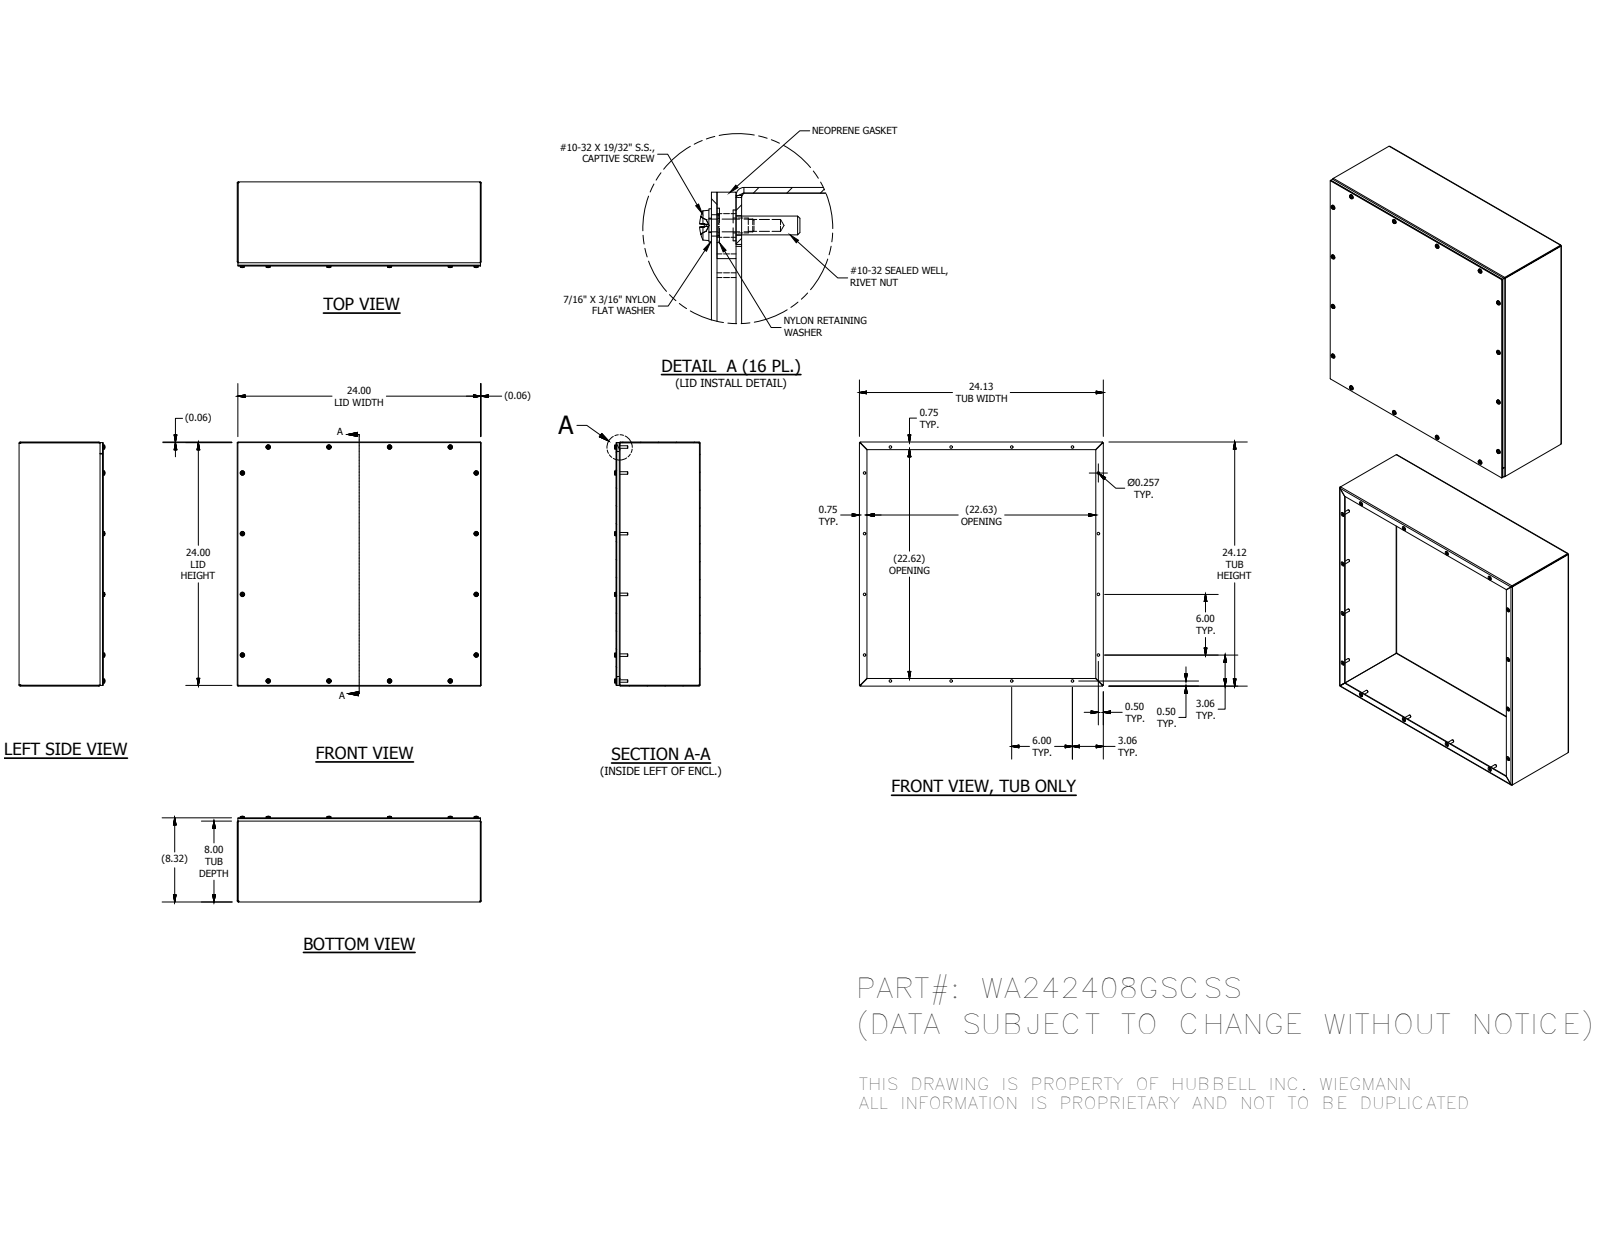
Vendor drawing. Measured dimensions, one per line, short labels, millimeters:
name: WA242408GSCSSBKP; WA2424GSCSSLID; 37210; 39035 (+4 more)
written by: Autodesk Inventor 2016 (AUTOMOTIVE_DESIGN)
unit: mm
bodies: 68 solids, 1412 faces (772 planar, 288 cylindrical, 352 other)
size: 612.77 × 612.77 × 215.35
volume: 2 736 000 mm³; area: 2 723 000 mm²
holes: 16× ⌀3.96, 16× ⌀4.78, 16× ⌀4.98, 16× ⌀6.53, 16× ⌀7.06, 16× ⌀7.14, 16× ⌀7.95
bosses: 16× ⌀11.51, 16× ⌀11.11, 16× ⌀10.31, 16× ⌀6.3, 16× ⌀4.25
rounds: 16× R2.27, 12× R0.79, 8× R1.78, 8× R2.67
face distances: 1.88, 209.55, 610.9, 211.43, 207.67, 612.78, 609.02, 201.32, 8.23, 6.35
hole spacings: 152.4, 304.8, 606.81, 227.02, 375.57, 429.08, 526.33, 565.76
